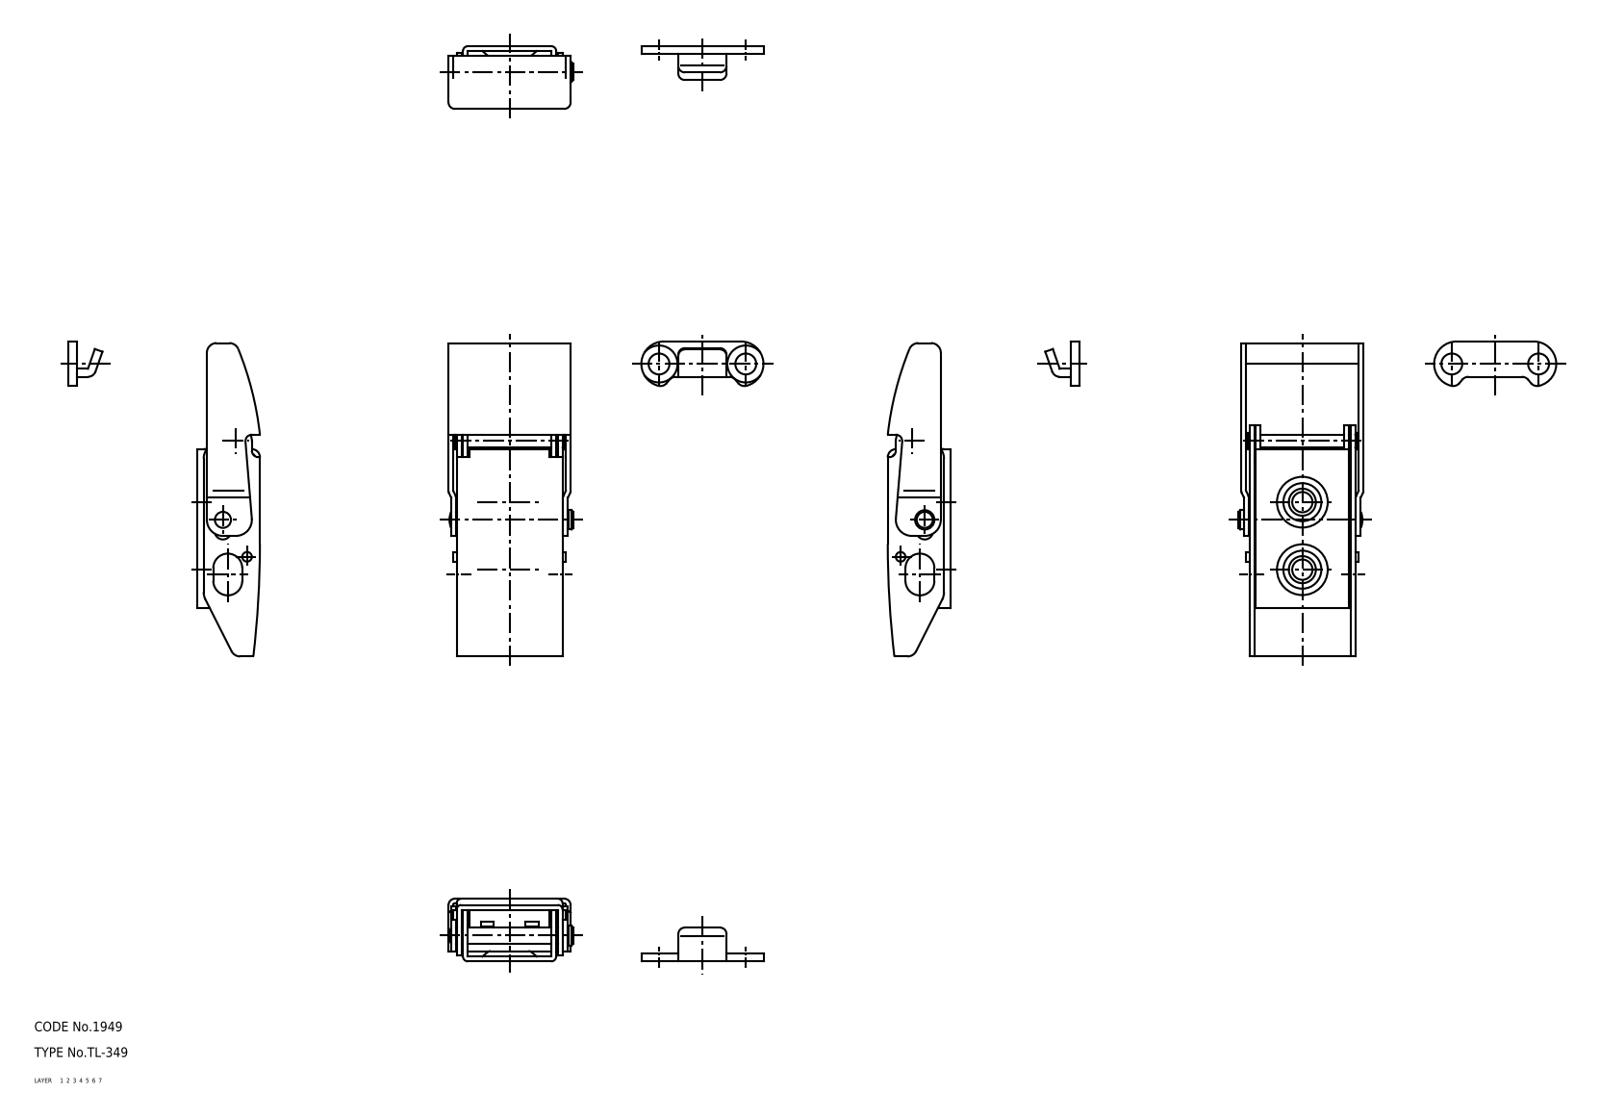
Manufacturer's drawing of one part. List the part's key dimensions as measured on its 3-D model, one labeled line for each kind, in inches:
Part name (STEP PRODUCT): 67129717; 67129730; 67129743; 67129756 (+5 more)
STEP written by: CADfix (AUTOMOTIVE_DESIGN)
Units: inches
Bodies: 9 solids, 331 faces (0 planar, 0 cylindrical, 331 other)
Overall size (bounding box): 3.858 × 1.528 × 0.768
Volume: 1.126 in³ · Surface area: 41.76 in²
